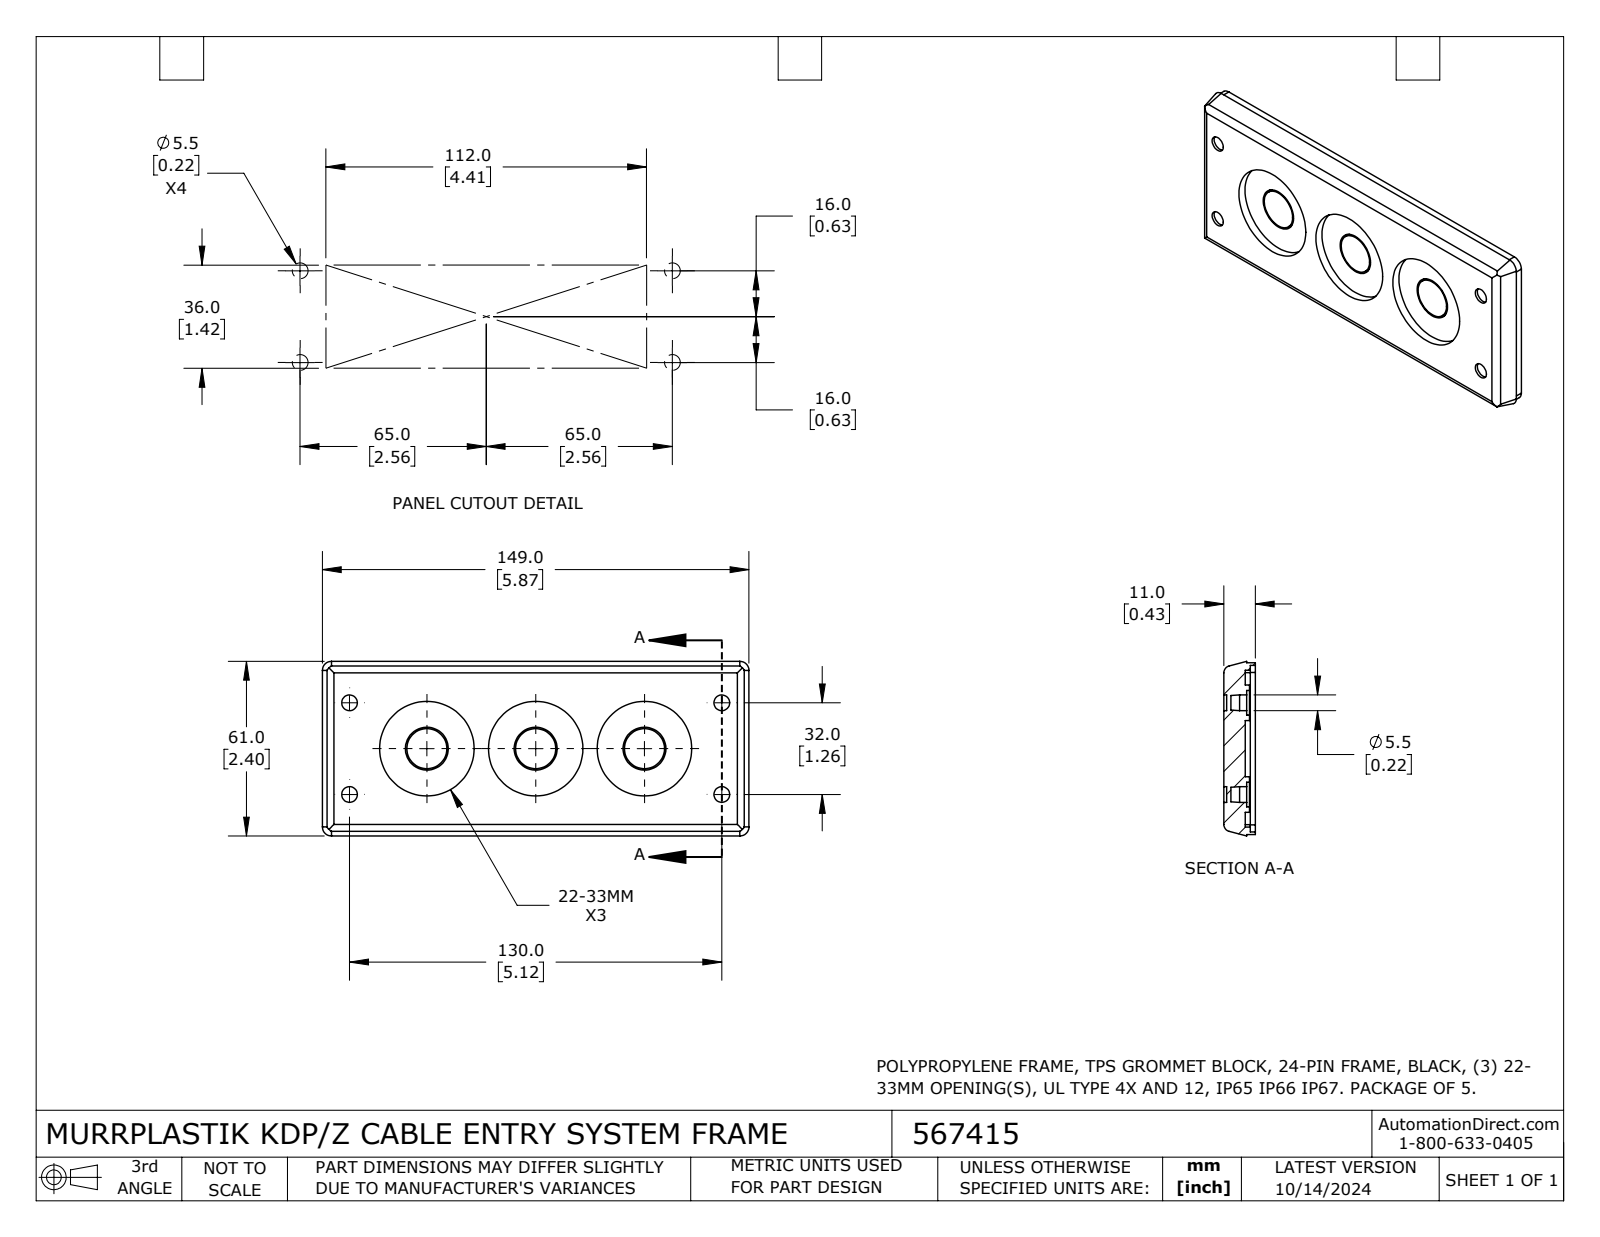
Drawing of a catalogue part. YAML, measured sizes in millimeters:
part_name: "567415"
step_written_by: "SolidWorks 2023 (CONFIG_CONTROL_DESIGN)"
units: millimeters
bodies: {solids: 1, faces: 160, planar: 60, cylindrical: 88, other: 12}
overall_size: [149, 61, 11]
volume: 46720
surface_area: 27650
round_holes:
  - {diameter: 5.5, count: 4}
  - {diameter: 8.6, count: 4}
  - {diameter: 15, count: 3}
  - {diameter: 33, count: 3}
round_bosses_or_shafts:
  - {diameter: 12.4, count: 4}
  - {diameter: 14, count: 3}
partial_cylinders:
  - {radius: 0.3, count: 16}
  - {radius: 0.9, count: 4}
  - {radius: 2.5, count: 4}
  - {radius: 2.5, count: 4}
  - {radius: 3.5, count: 4}
  - {radius: 7.7, count: 4}
face_to_face_distances: [5.5, 2.5, 3, 2, 4.5, 7.5, 1.7, 11, 8.8, 51.2]
hole_center_spacings: [31.4, 66.9, 104.2, 32, 38, 130, 133.9, 76]
